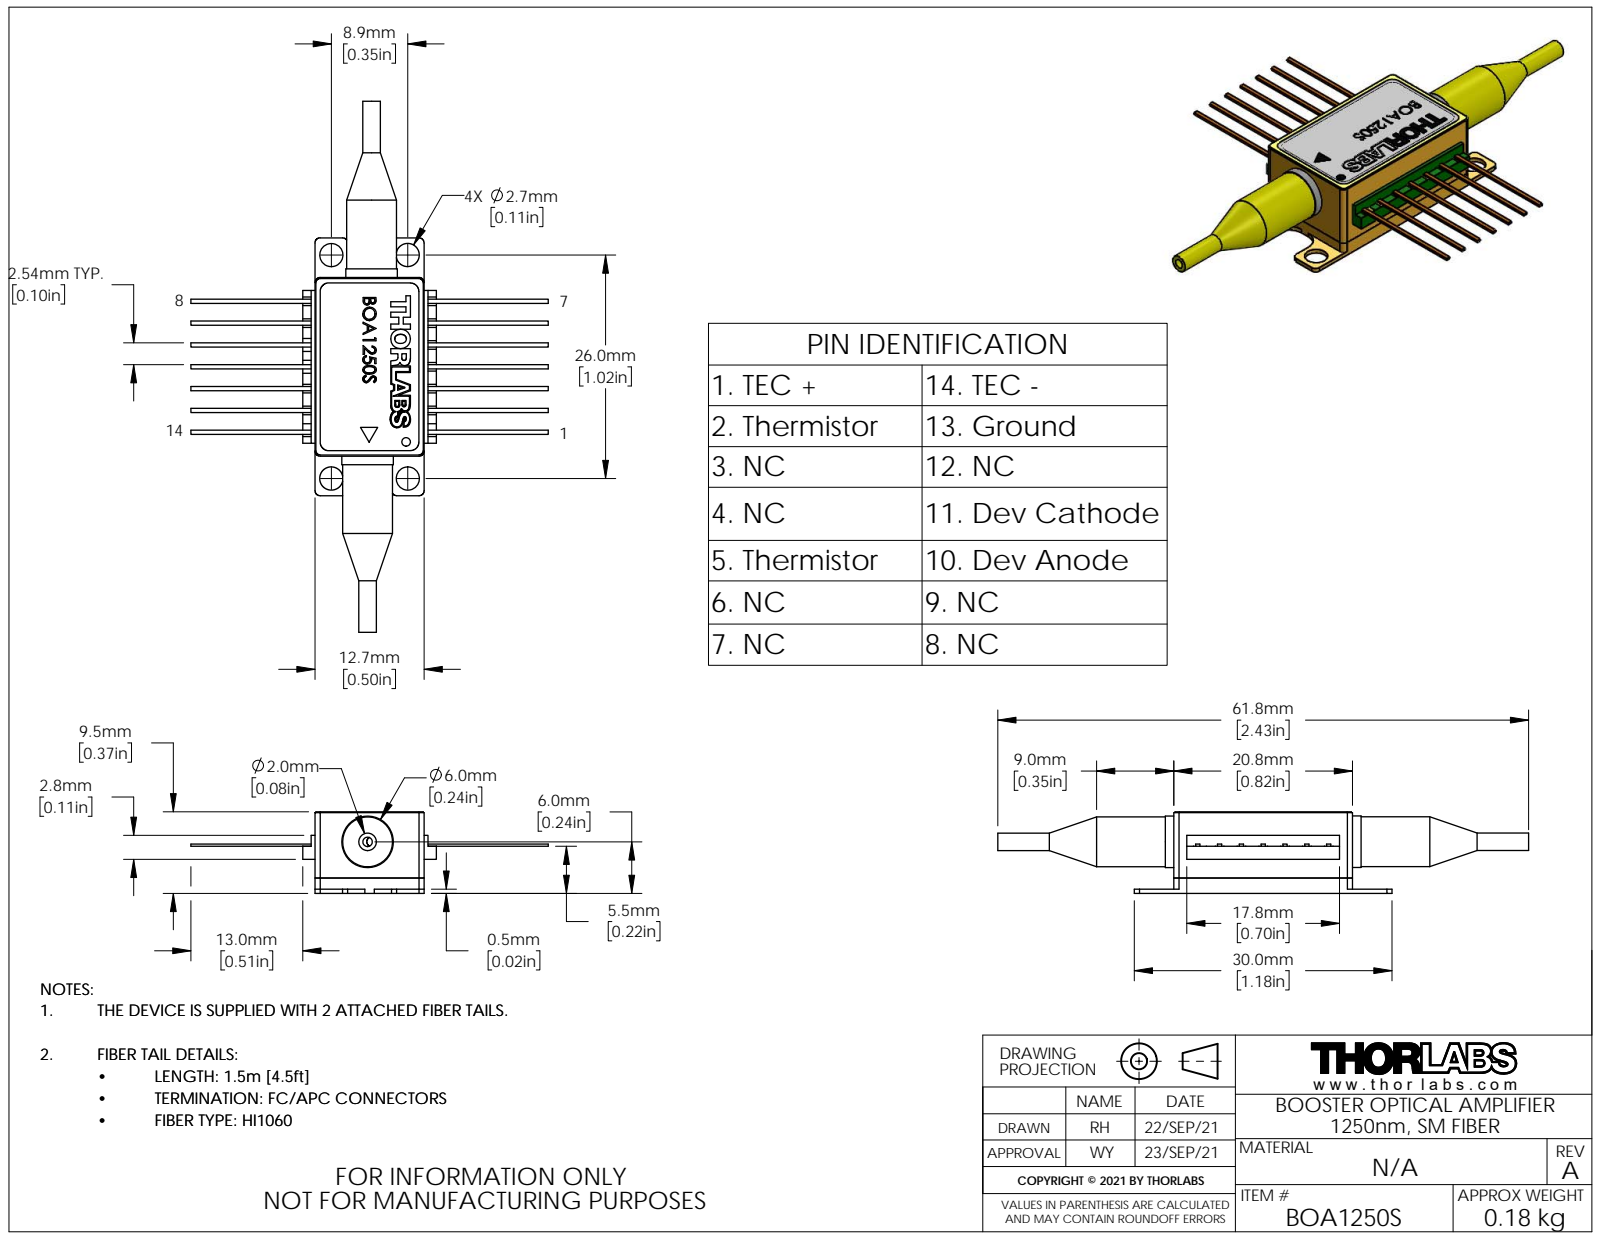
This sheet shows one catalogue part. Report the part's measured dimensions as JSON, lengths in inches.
{"part_name": "QTN042709-E0W", "step_written_by": "SolidWorks 2018 (AUTOMOTIVE_DESIGN)", "units": "inches", "bodies": {"solids": 0, "faces": 335, "planar": 241, "cylindrical": 50, "other": 44}, "overall_size": [2.433, 1.638, 0.374], "round_holes": [[0.106, 4], [0.043, 2], [0.039, 1]], "round_bosses_or_shafts": [[0.236, 2], [0.228, 2], [0.08, 2]], "partial_cylinders_radius": [[0.024, 12], [0.02, 4], [0.079, 4]], "face_to_face_distances": [0.373, 0.5, 0.071, 0.302, 0.06, 0.216, 0.145, 0.157, 0.156, 0.085], "hole_center_spacings": [0.35, 1.024, 1.082, 0.019, 0.168, 0.381, 0.856, 0.922]}
